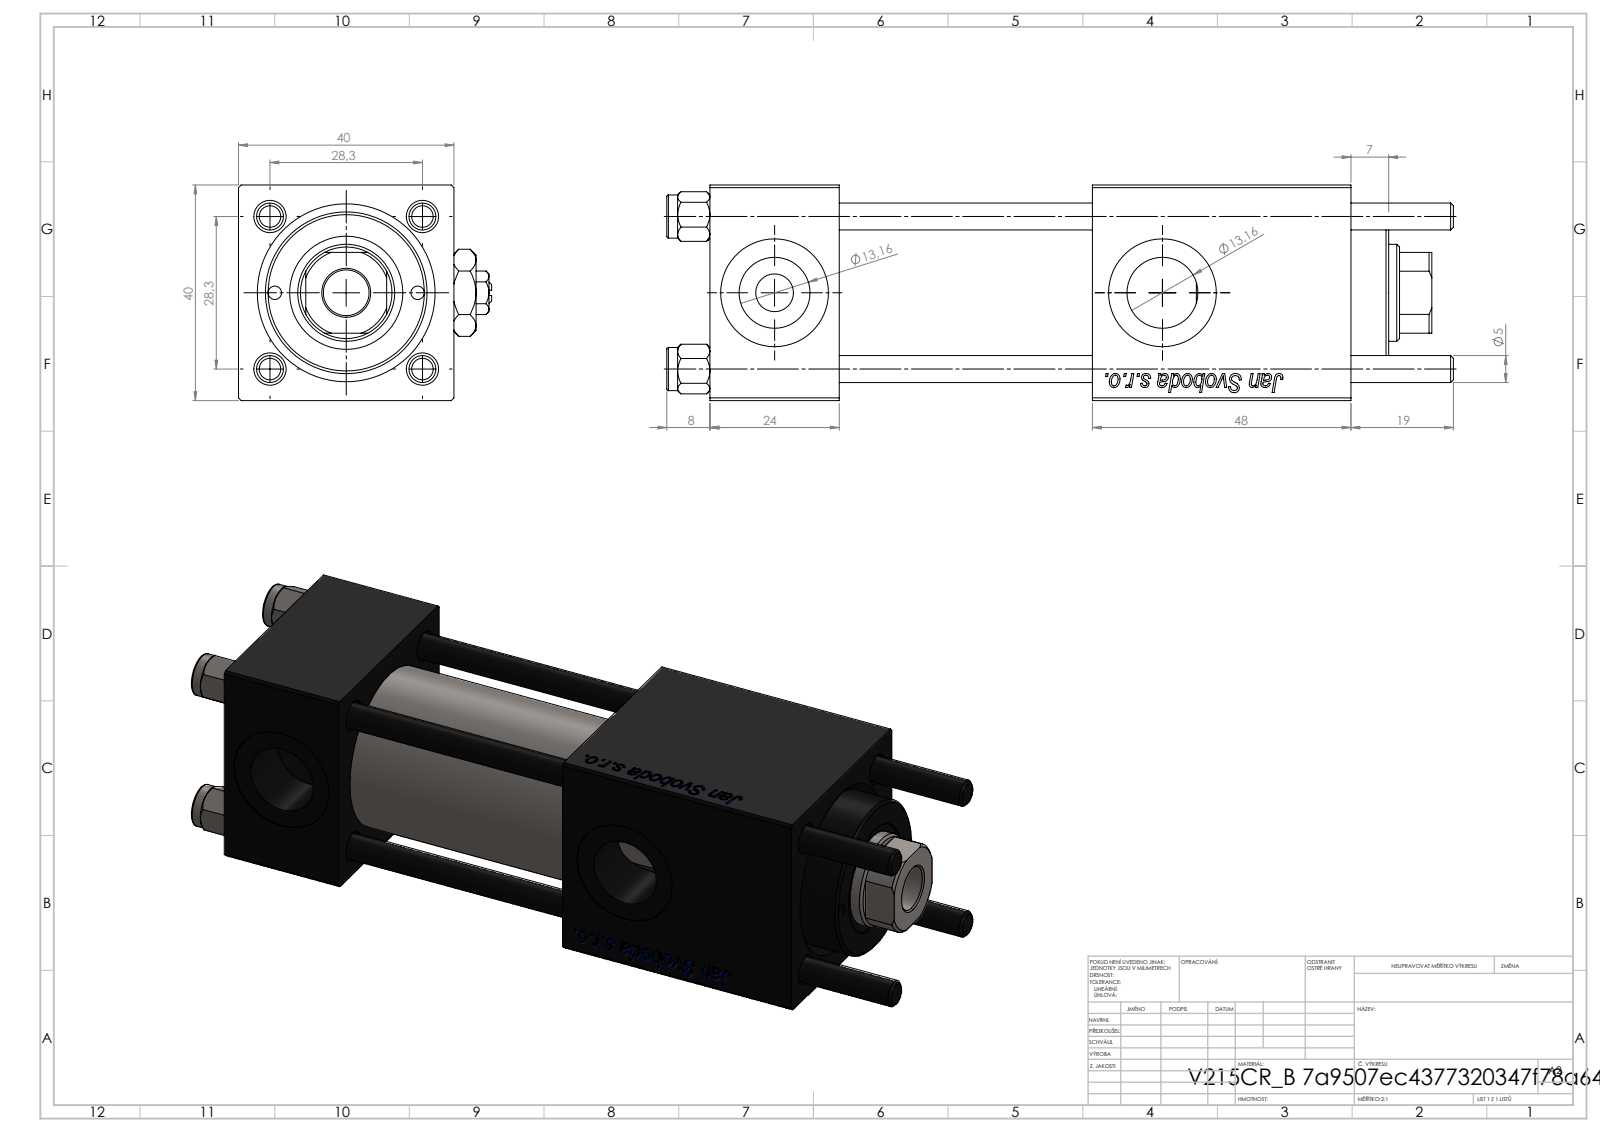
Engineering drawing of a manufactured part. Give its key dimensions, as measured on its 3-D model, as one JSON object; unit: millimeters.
{"part_name": "V215_VC_A; V215CR_B_TYCINKA; V215CR_VCP_B; NUT_M5_B (+2 more)", "step_written_by": "SolidWorks 2019 (CONFIG_CONTROL_DESIGN)", "units": "millimeters", "bodies": {"solids": 13, "faces": 1259, "planar": 477, "cylindrical": 92, "other": 690}, "overall_size": [146, 47, 40], "volume_mm3": 150970, "surface_area_mm2": 62850, "round_holes": [[5, 4], [20, 3], [2.5, 2], [7, 2], [13.16, 2], [8.5, 1], [18, 1], [21, 1], [25, 1], [30, 1]], "round_bosses_or_shafts": [[8, 4], [31, 1]], "partial_cylinders_radius": [[8.5, 1]], "face_to_face_distances": [40, 24, 39.8, 47, 71, 90.3, 66.3, 19.3, 119, 95], "hole_center_spacings": [14.18, 20.01, 28.3, 30.84, 13.25, 40.02, 26.5, 72]}
